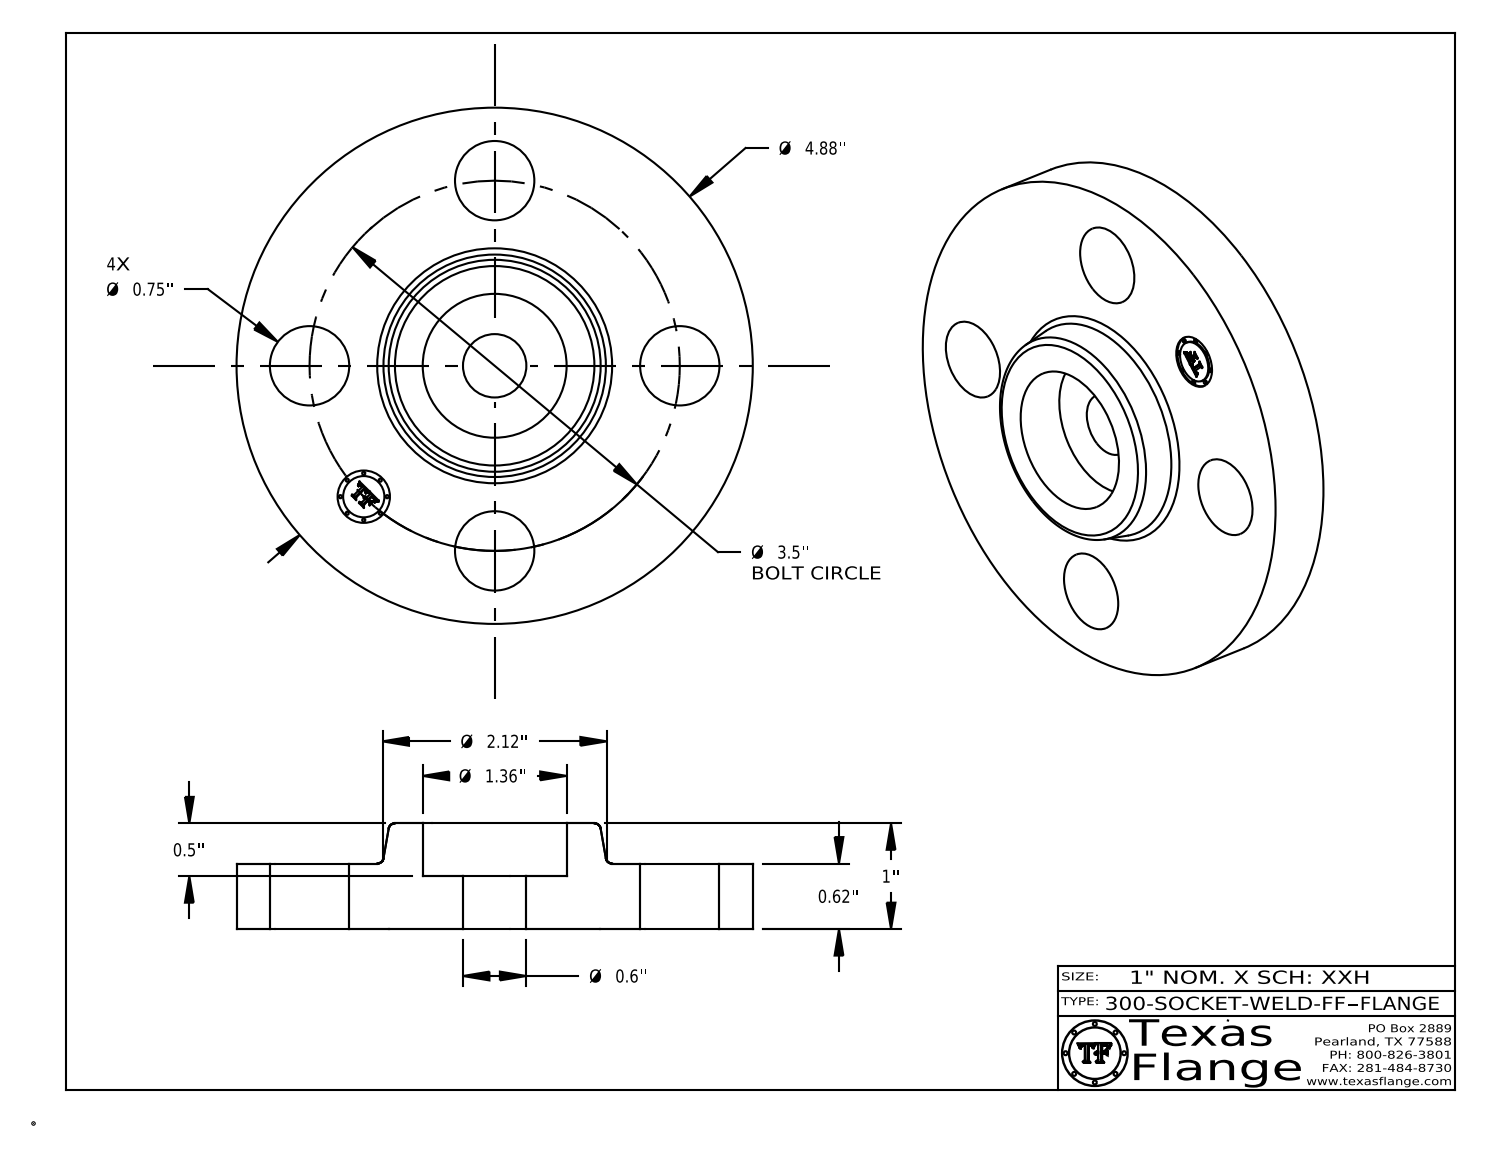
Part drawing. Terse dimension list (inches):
name: 300-SOCKET-WELD-FF
written by: CATIA V5 STEP AP214 (AUTOMOTIVE_DESIGN)
unit: in
bodies: 1 solid, 410 faces (370 planar, 34 cylindrical, 6 other)
size: 4.88 × 4.88 × 1
volume: 10.89 in³; area: 53.67 in²
holes: 4× ⌀0.75, 1× ⌀0.495, 1× ⌀0.599, 1× ⌀1.36
bosses: 8× ⌀0.03, 1× ⌀4.88, 1× ⌀0.39
face distances: 0.62, 0.5, 1, 0.38, 0.12, 0.105, 0.015, 0.605, 0.395, 0.148
hole spacings: 1.75, 2.475, 1.339, 3.233, 3.5
